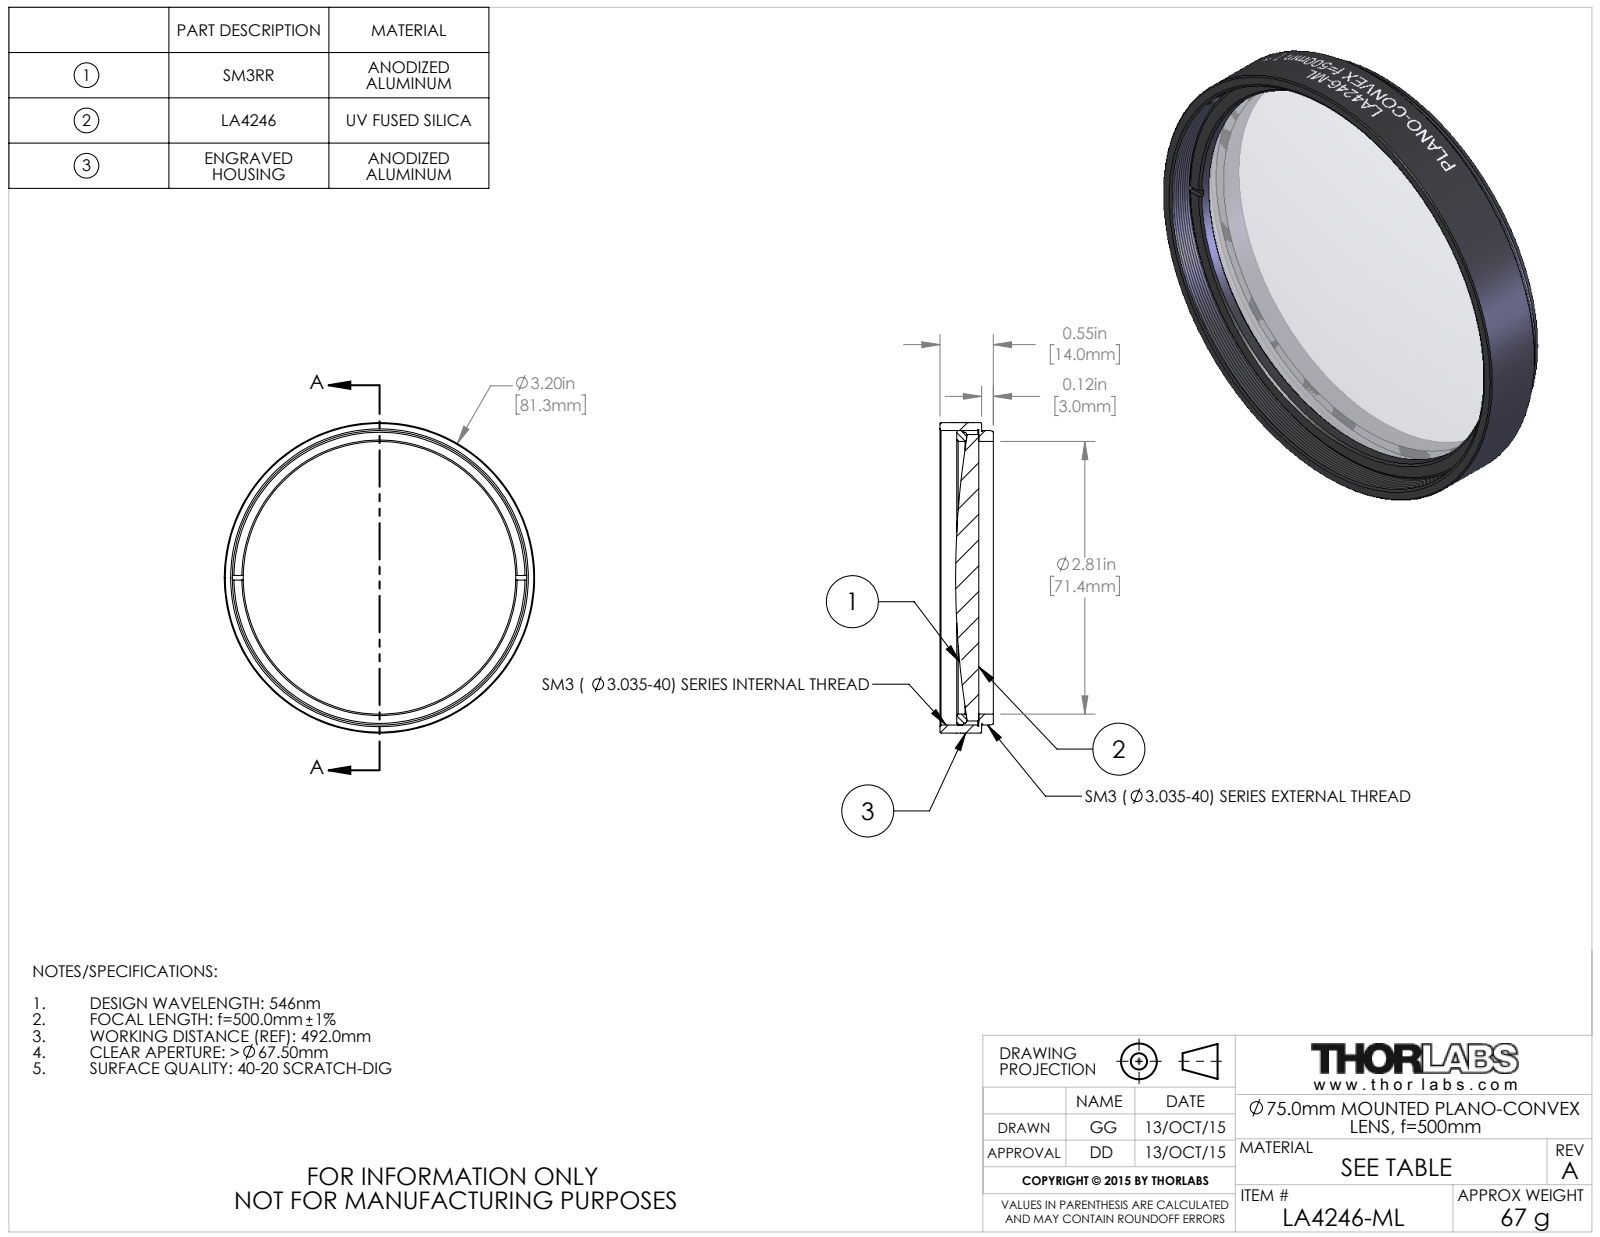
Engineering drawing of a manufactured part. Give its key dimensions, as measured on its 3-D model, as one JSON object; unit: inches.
{"part_name": "TTN039222-E0W", "step_written_by": "SolidWorks 2016 (CONFIG_CONTROL_DESIGN)", "units": "inches", "bodies": {"solids": 3, "faces": 117, "planar": 17, "cylindrical": 76, "other": 24}, "overall_size": [3.2, 3.2, 0.55], "volume_in3": 1.815, "surface_area_in2": 32.76, "round_holes": [[2.81, 1], [3.055, 1]], "round_bosses_or_shafts": [[3.2, 1], [3.035, 1], [3.015, 1], [2.998, 1], [2.953, 1]], "face_to_face_distances": [0.15, 0.12, 0.03, 0.377, 0.257, 0.227, 0.277, 0.157, 0.127, 0.1]}
